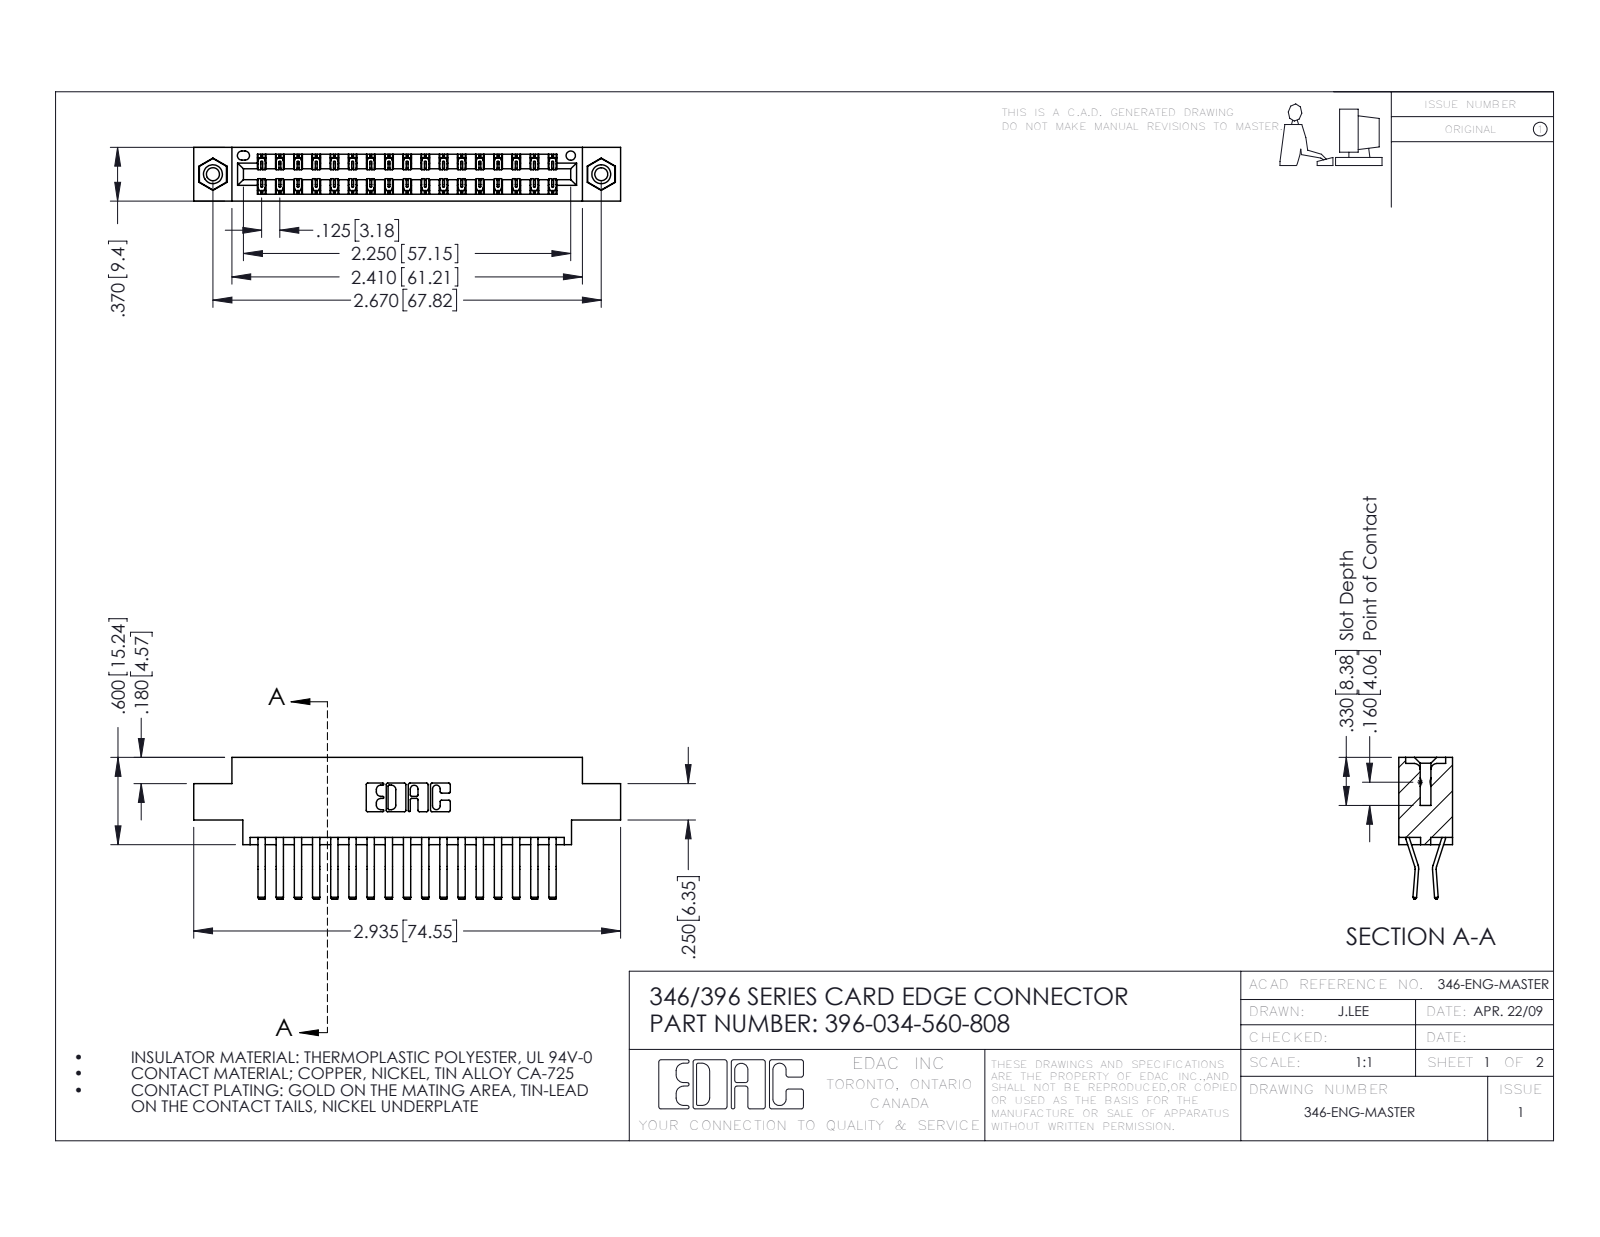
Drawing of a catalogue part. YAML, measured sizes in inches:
part_name: "345-250-001_345-250-003-102; 345-292-001_560 Tail; 396-034-560-808; 346 Part_0.170 Offset - 0.156 Dia-TI"
step_written_by: "SolidWorks 2016 (CONFIG_CONTROL_DESIGN)"
units: inches
bodies: {solids: 37, faces: 2022, planar: 1302, cylindrical: 704, other: 16}
overall_size: [2.935, 0.975, 0.37]
volume: 0.436
surface_area: 15.83
round_holes:
  - {diameter: 0.089, count: 2}
  - {diameter: 0.125, count: 2}
  - {diameter: 0.156, count: 2}
  - {diameter: 0.064, count: 1}
round_bosses_or_shafts:
  - {diameter: 0.155, count: 2}
partial_cylinders:
  - {radius: 0.006, count: 51}
  - {radius: 0.01, count: 22}
  - {radius: 0.007, count: 6}
  - {radius: 0.031, count: 6}
  - {radius: 0.026, count: 3}
  - {radius: 0.01, count: 2}
  - {radius: 0.014, count: 2}
  - {radius: 0.022, count: 2}
face_to_face_distances: [0.048, 0.322, 0.37, 0.25, 0.025, 0.072, 0.298, 0.275, 0.222, 0.148]
hole_center_spacings: [0.246, 2.463, 2.67]
